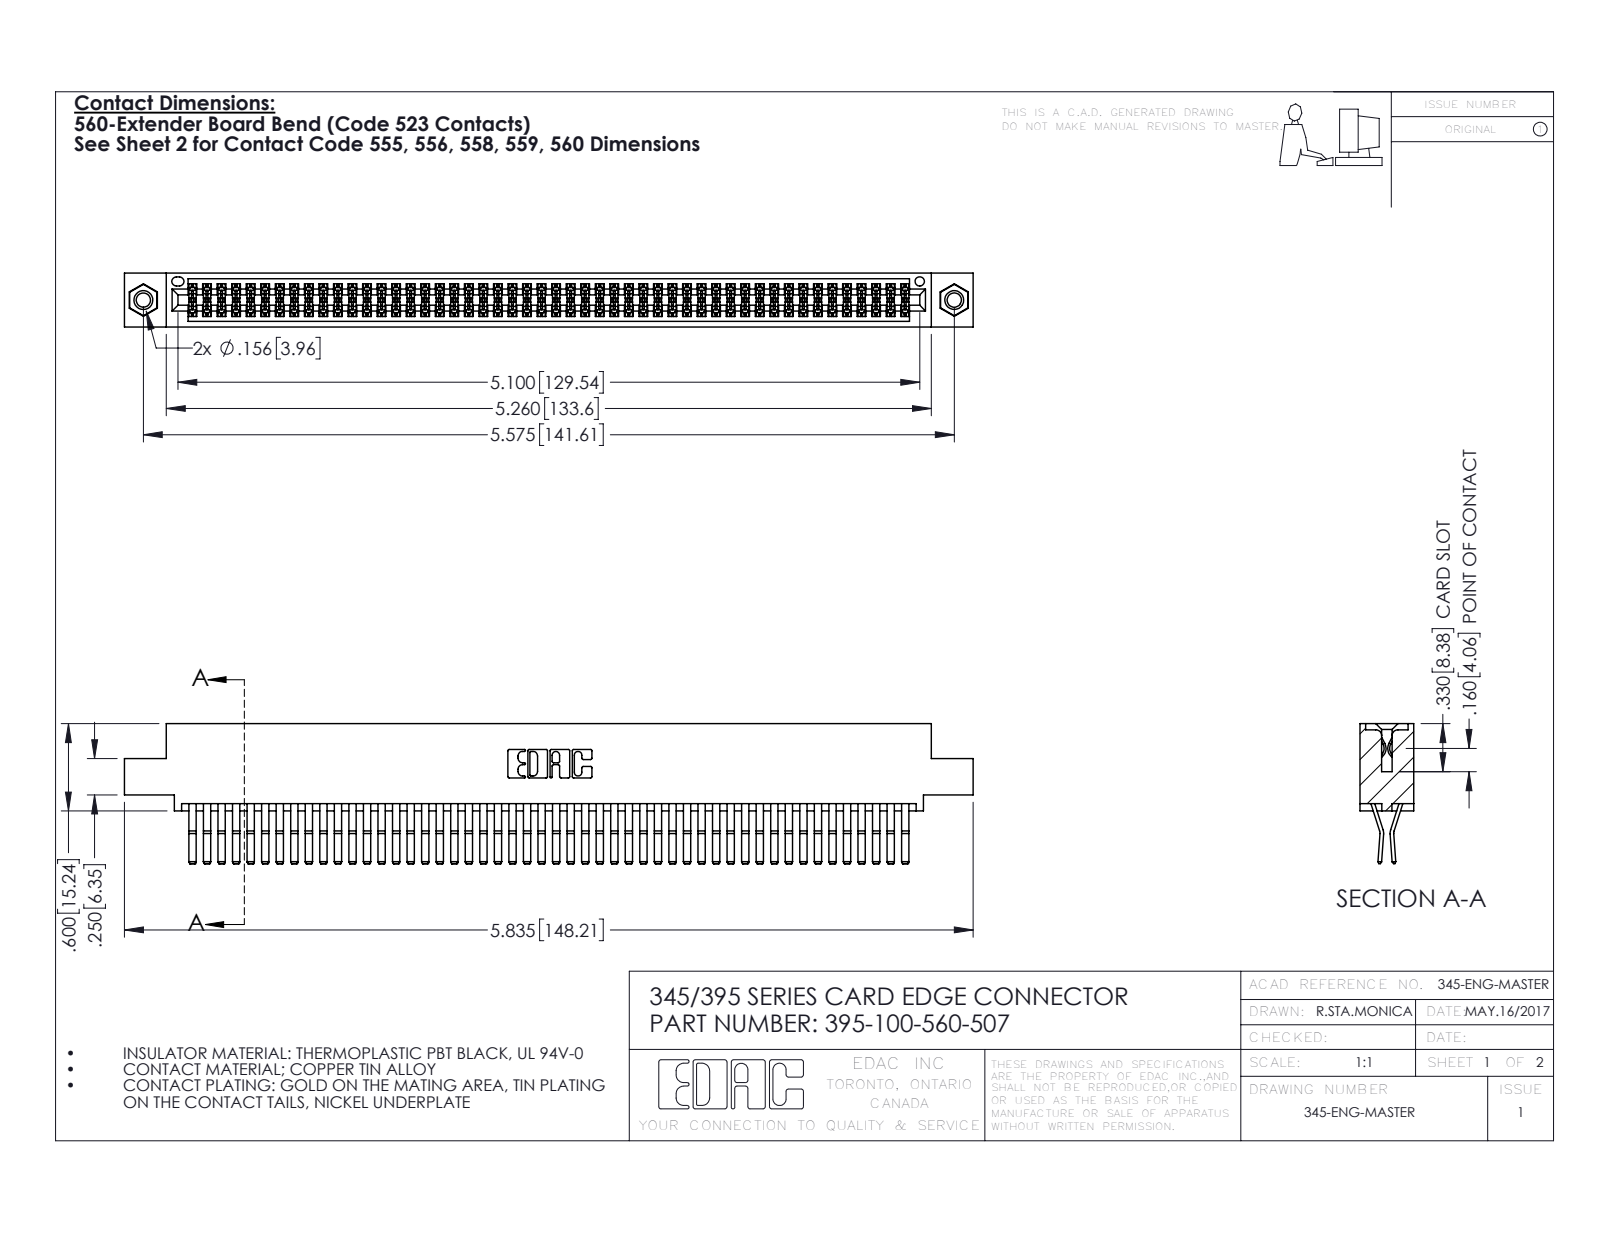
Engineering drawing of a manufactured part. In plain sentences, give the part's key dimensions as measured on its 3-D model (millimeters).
The part is named "395-100-560-507; 345 Part_0.110 Offset - 0.156 Dia-TI; 345-250-001_345-250-005-103; 345-292-001_560 Tail". Its 3-D file was written by "SolidWorks 2016 (CONFIG_CONTROL_DESIGN)". It is 103 solids with 5390 faces: 3416 planar, 1958 cylindrical and 16 other. Overall it measures 148.2 by 24.4 by 9.4 millimeters. Its volume is 15 000 cubic millimeters and its surface area 24 190 square millimeters. Round holes: 2 of diameter 2.5, 2 of diameter 3.2, 2 of diameter 4, 1 of diameter 1.6. Round bosses or shafts: 2 of diameter 3.9. Partial cylindrical surfaces (rounded edges, fillets, slot ends): 151 of radius 0.2, 22 of radius 0.3, 6 of radius 0.2, 6 of radius 0.8, 3 of radius 0.7, 2 of radius 0.3, 2 of radius 0.4, 2 of radius 0.5. The main face-to-face distances are 0.6, 1.8, 7.6, 9.4, 5.1, 2.5, 6.9, 5.7, 4.4, 3.8. The hole center spacings are 6.9, 135.6, 141.6.
